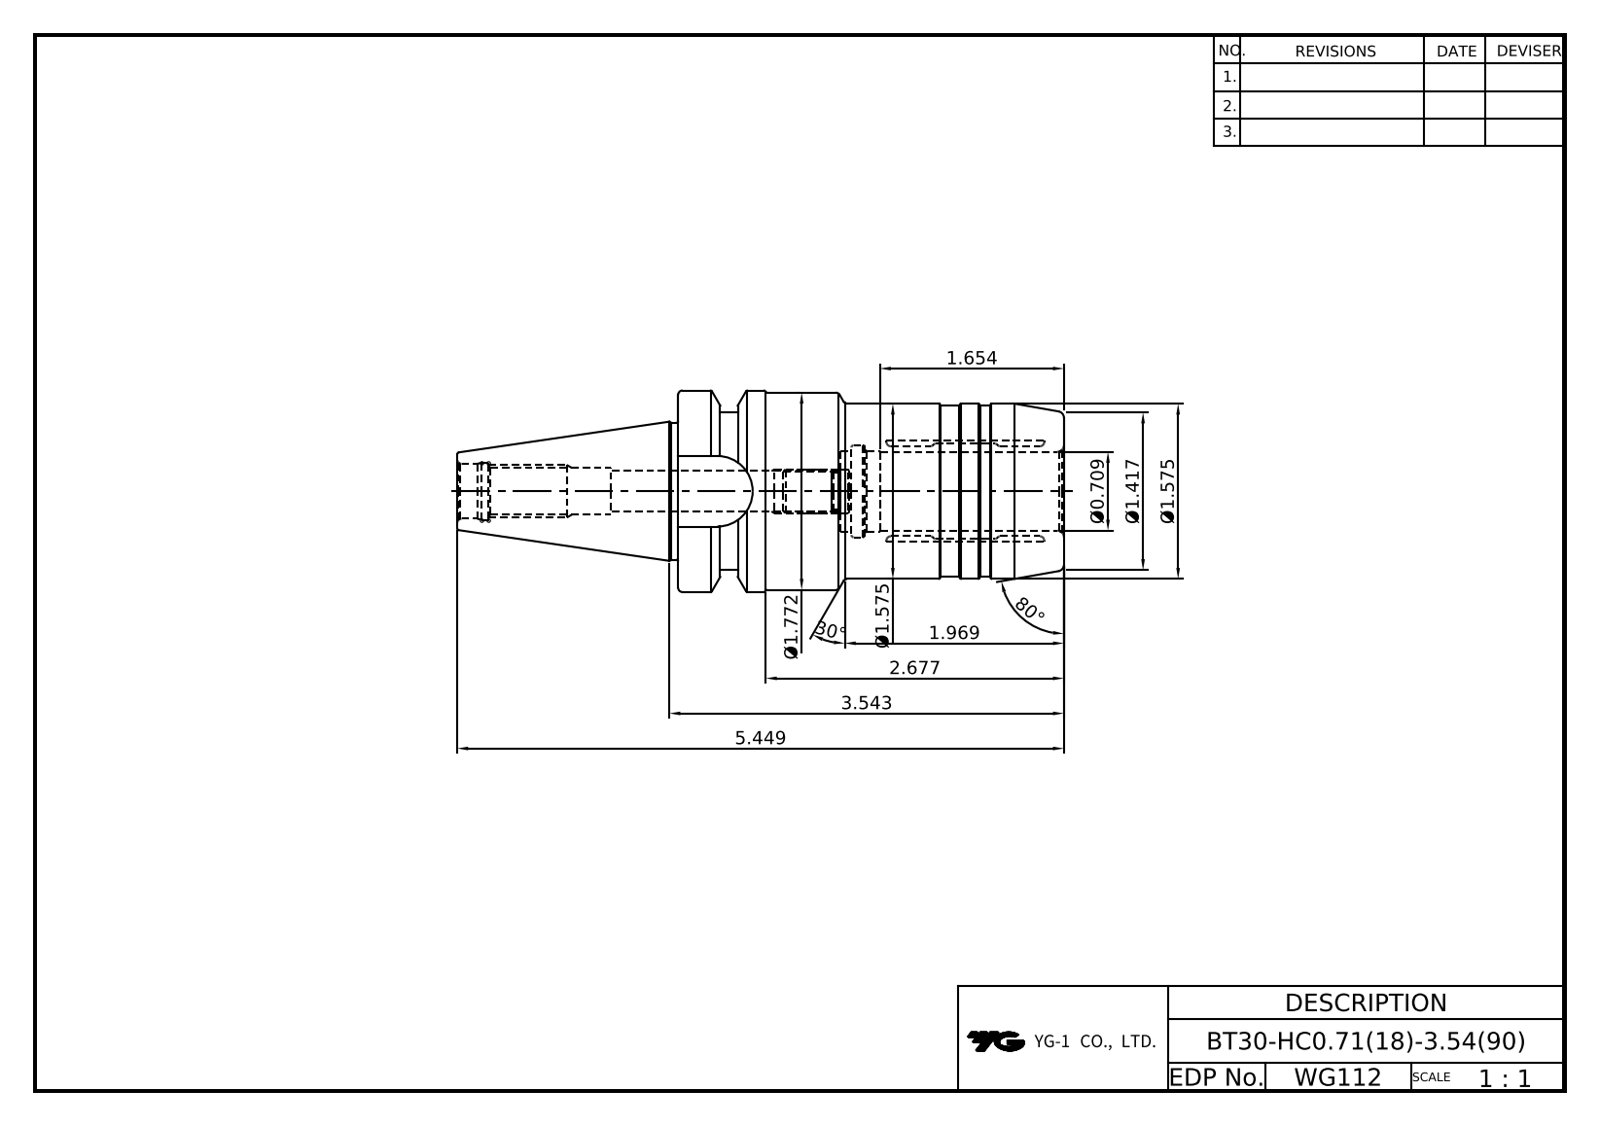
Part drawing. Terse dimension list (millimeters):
name: LO-BT30ADB-HC18-90
written by: Autodesk Inventor 2022 (AUTOMOTIVE_DESIGN)
unit: mm
bodies: 1 solid, 93 faces (20 planar, 38 cylindrical, 35 other)
size: 138.4 × 46 × 46
volume: 121 658 mm³; area: 24 571 mm²
holes: 4× ⌀3.24, 4× ⌀4, 1× ⌀8.92, 1× ⌀10.11, 1× ⌀12.5, 1× ⌀13.1, 1× ⌀18, 1× ⌀18.4
bosses: 1× ⌀46, 1× ⌀44.5, 1× ⌀40, 1× ⌀39, 1× ⌀31.2
rounds: 1× R8.05, 1× R18
face distances: 88, 32.6, 37, 51, 13.6, 23.4, 74.4, 9.6, 4, 27.4
